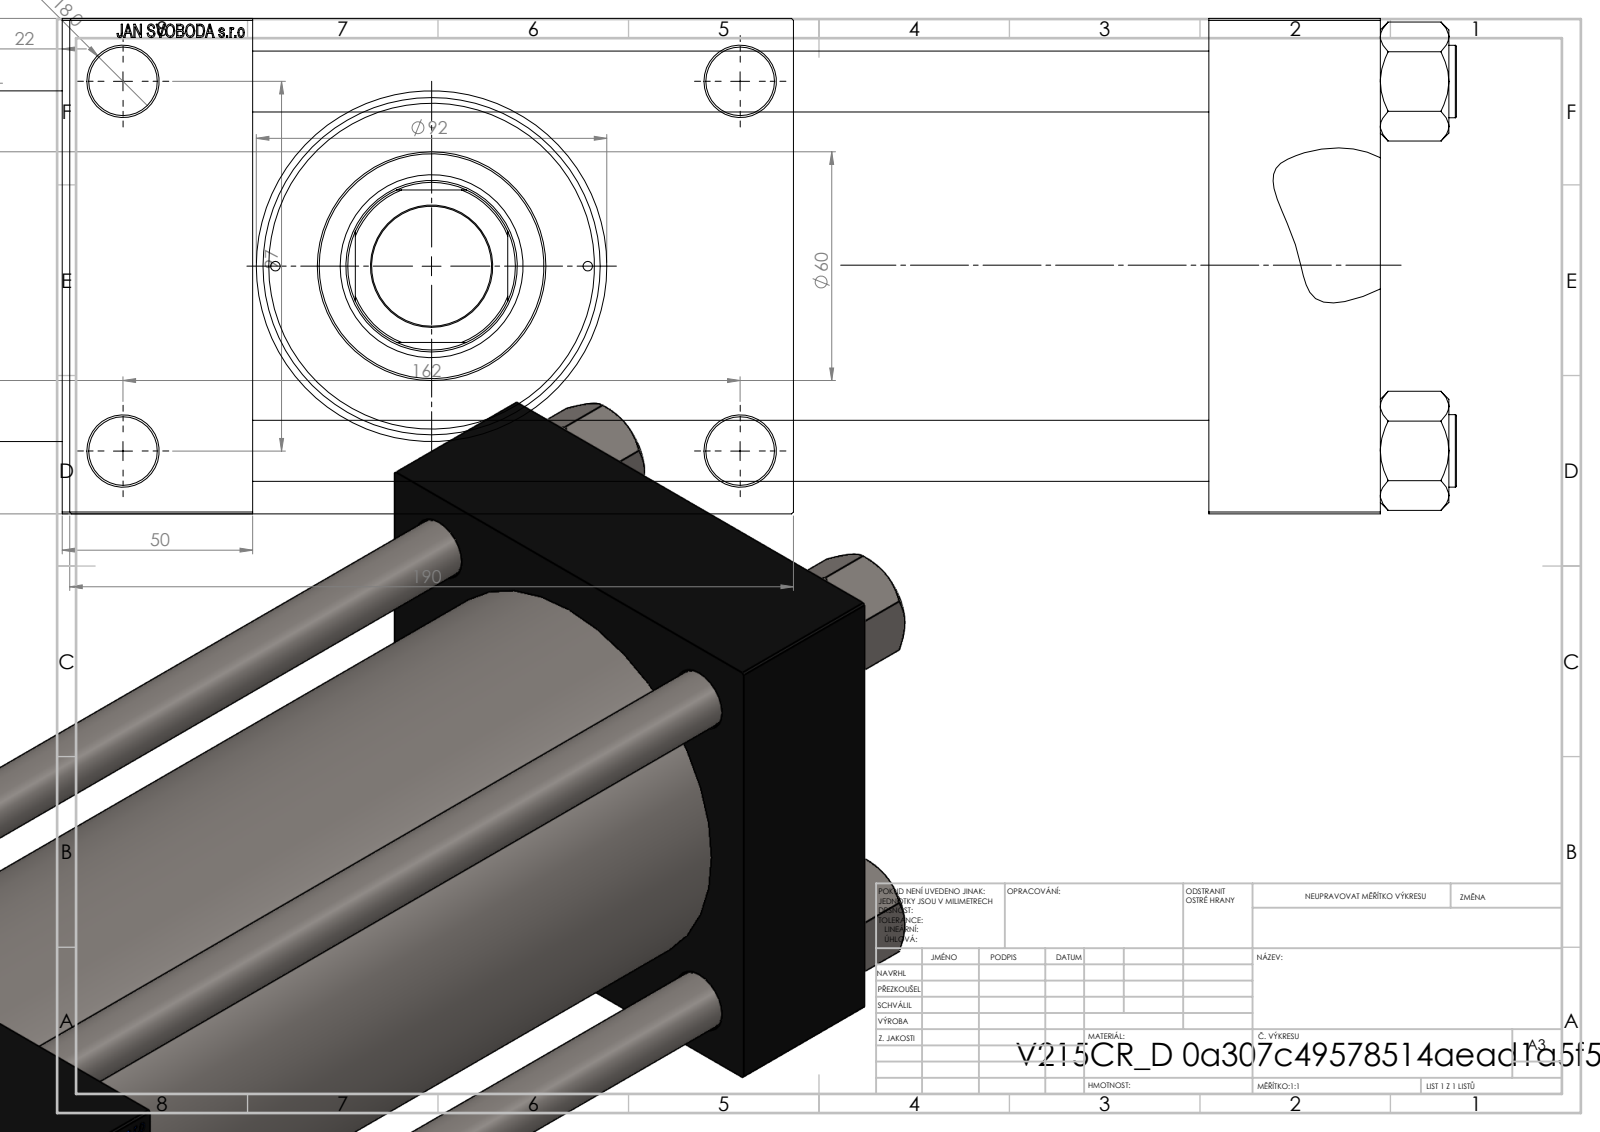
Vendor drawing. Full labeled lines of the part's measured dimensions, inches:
Part name (STEP PRODUCT): V215CR_VCP_D; V215_VC_A; V215CR_D_Body; NUT_M5_D (+1 more)
STEP written by: SolidWorks 2019 (CONFIG_CONTROL_DESIGN)
Units: inches
Bodies: 11 solids, 1159 faces (547 planar, 92 cylindrical, 520 other)
Overall size (bounding box): 16.654 × 7.48 × 5.118
Volume: 195 in³ · Surface area: 825.9 in²
Round holes (diameter × count): ⌀0.63 ×4, ⌀0.709 ×4, ⌀0.098 ×2, ⌀0.276 ×2, ⌀1.041 ×2, ⌀1.378 ×2, ⌀1.24 ×1, ⌀1.772 ×1, ⌀1.89 ×1, ⌀2.992 ×1, ⌀3.366 ×1, ⌀3.937 ×1
Round bosses / shafts (diameter × count): ⌀0.748 ×4, ⌀4.173 ×1, ⌀3.622 ×1, ⌀2.362 ×1
Partial cylindrical surfaces — rounded edges, fillets, slot ends (radius × count): R0.866 ×1
Main face-to-face distances: 5.118, 1.772, 11.654, 9.882, 13.622, 11.85, 1.969, 1.181, 6.299, 3.78
Hole centre spacings: 1.281, 1.93, 2.475, 2.698, 3.717, 3.815, 4.005, 4.026
